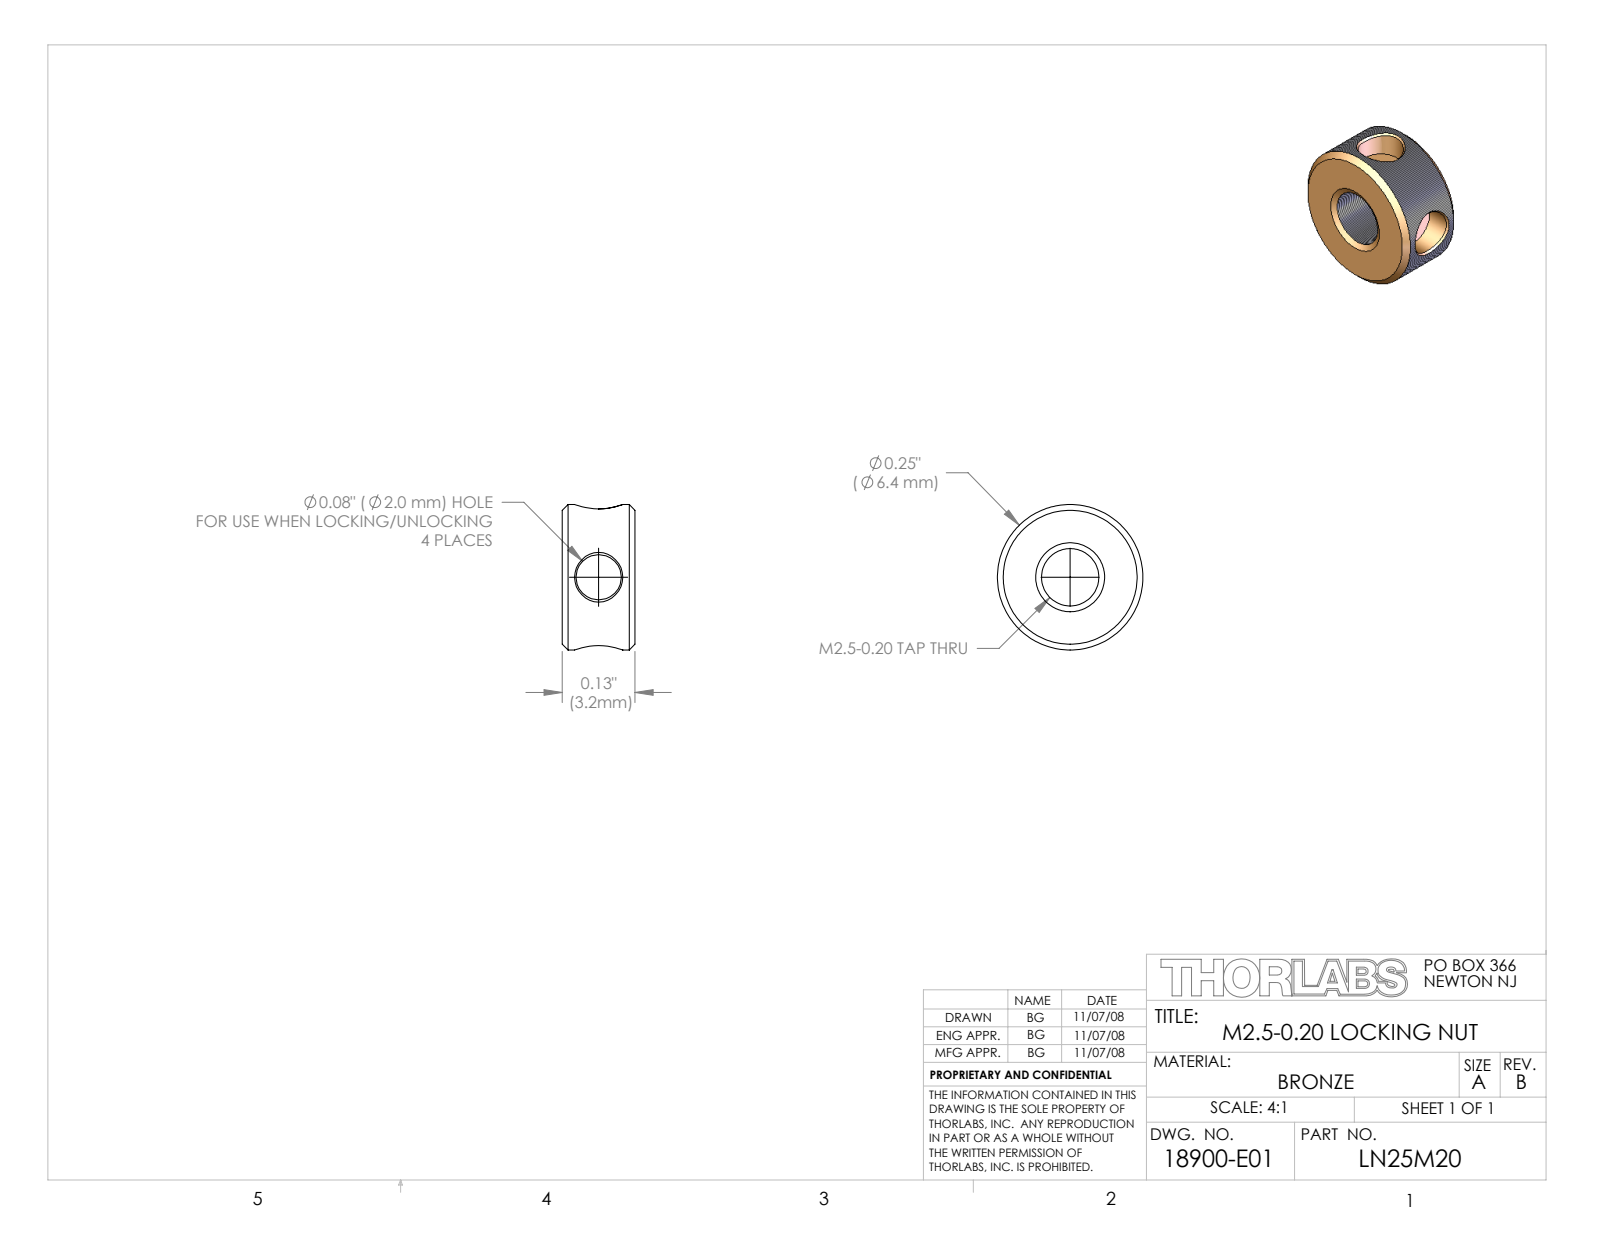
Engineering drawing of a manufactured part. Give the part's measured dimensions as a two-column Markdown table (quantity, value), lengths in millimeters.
| quantity | value |
| --- | --- |
| part name | 18900-E0W |
| STEP written by | SolidWorks 2007 (AUTOMOTIVE_DESIGN) |
| units | millimeters |
| bodies | 1 solid, 34 faces (6 planar, 12 cylindrical, 16 other) |
| overall size | 6.35 × 6.35 × 3.17 |
| volume | 70 mm³ |
| surface area | 159 mm² |
| round holes (diameter × count) | 1.98 × 2, 2.5 × 1 |
| round bosses / shafts (diameter × count) | 6.35 × 1 |
| main face-to-face distances | 3.18, 4.06 |
